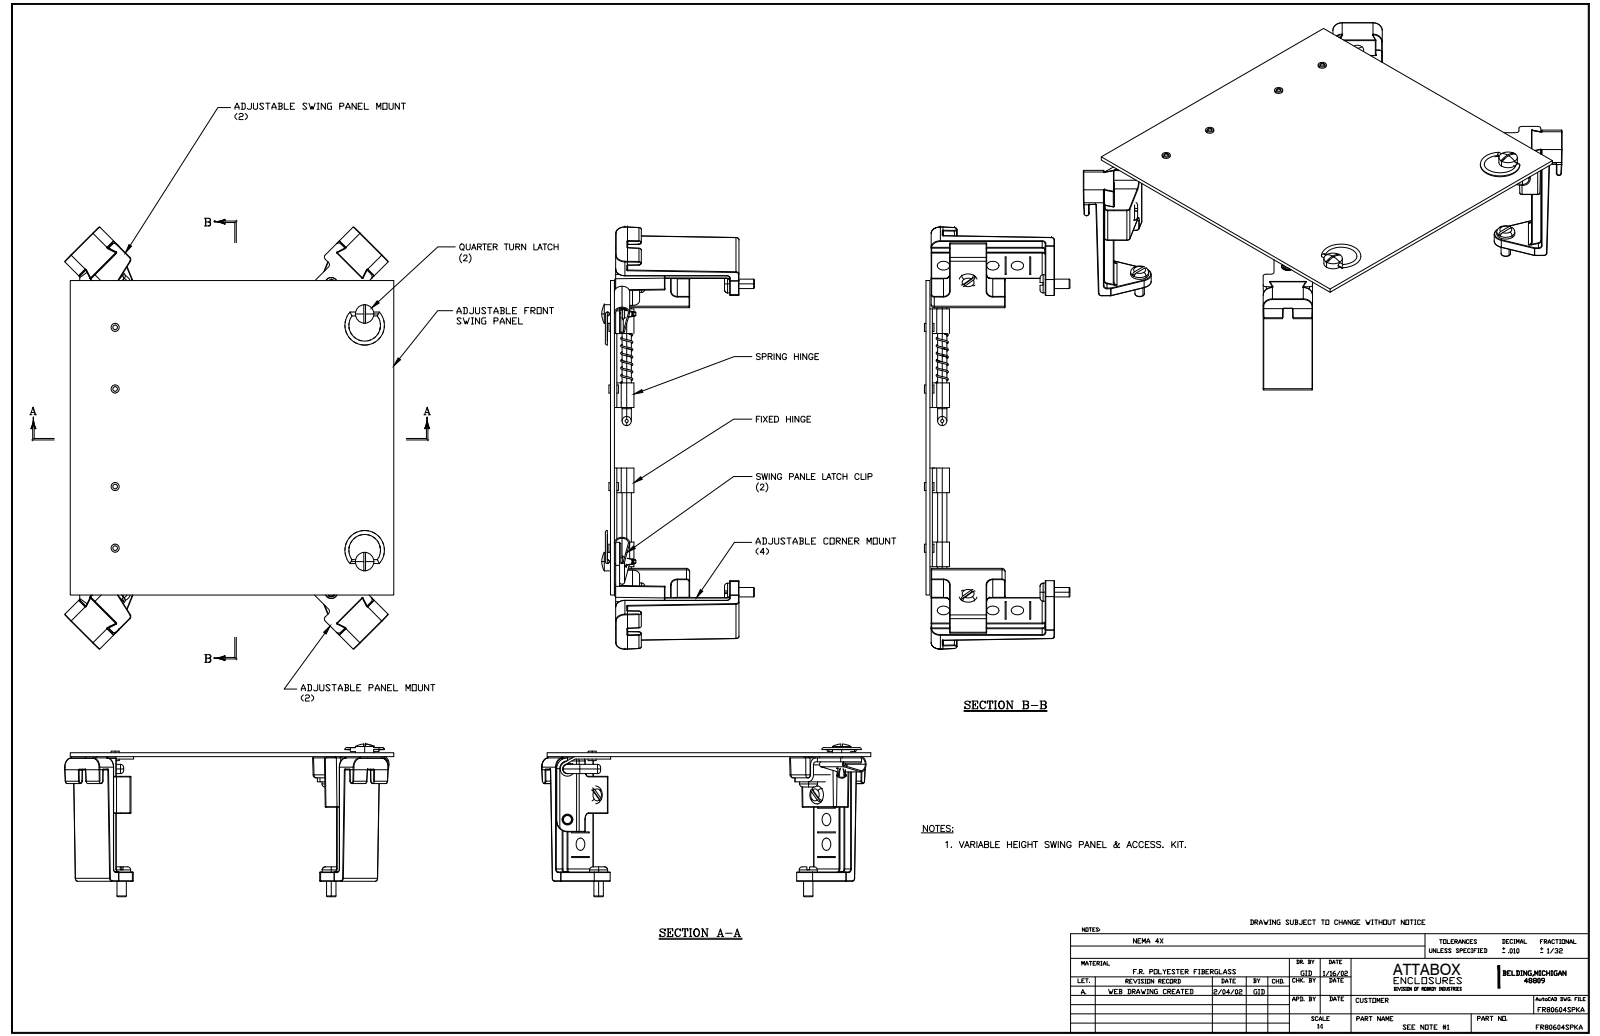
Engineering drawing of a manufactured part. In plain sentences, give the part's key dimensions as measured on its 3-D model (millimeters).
The part is named "FR80604SPKA". Its 3-D file was written by "SolidWorks 2019 (AUTOMOTIVE_DESIGN)". It is 48 solids with 1445 faces: 586 planar, 465 cylindrical and 394 other. Overall it measures 217.3 by 166.7 by 68.7 millimeters. Its volume is 161 400 cubic millimeters and its surface area 122 400 square millimeters. Round holes: 20 of diameter 6.4, 6 of diameter 4, 6 of diameter 6.4, 4 of diameter 1.3, 4 of diameter 3.6, 4 of diameter 3.7, 4 of diameter 5.5, 4 of diameter 5.6, 3 of diameter 7.9, 2 of diameter 5, 2 of diameter 8.9, 1 of diameter 3.9. Round bosses or shafts: 10 of diameter 4.8, 6 of diameter 9.5, 6 of diameter 6.2, 4 of diameter 11, 4 of diameter 8, 4 of diameter 4.1, 4 of diameter 2, 2 of diameter 10. Partial cylindrical surfaces (rounded edges, fillets, slot ends): 212 of radius 0.3, 44 of radius 1.5, 12 of radius 1.6, 8 of radius 0.6, 6 of radius 1.6, 6 of radius 3.3, 4 of radius 1.2, 4 of radius 4.8. The main face-to-face distances are 2, 2, 215.1, 5.2, 220.2, 4.8, 25.4, 58.8, 63.6, 2.5. The hole center spacings are 38.1, 12.7, 22.1, 25.4, 35.9, 44, 144, 52.3.
